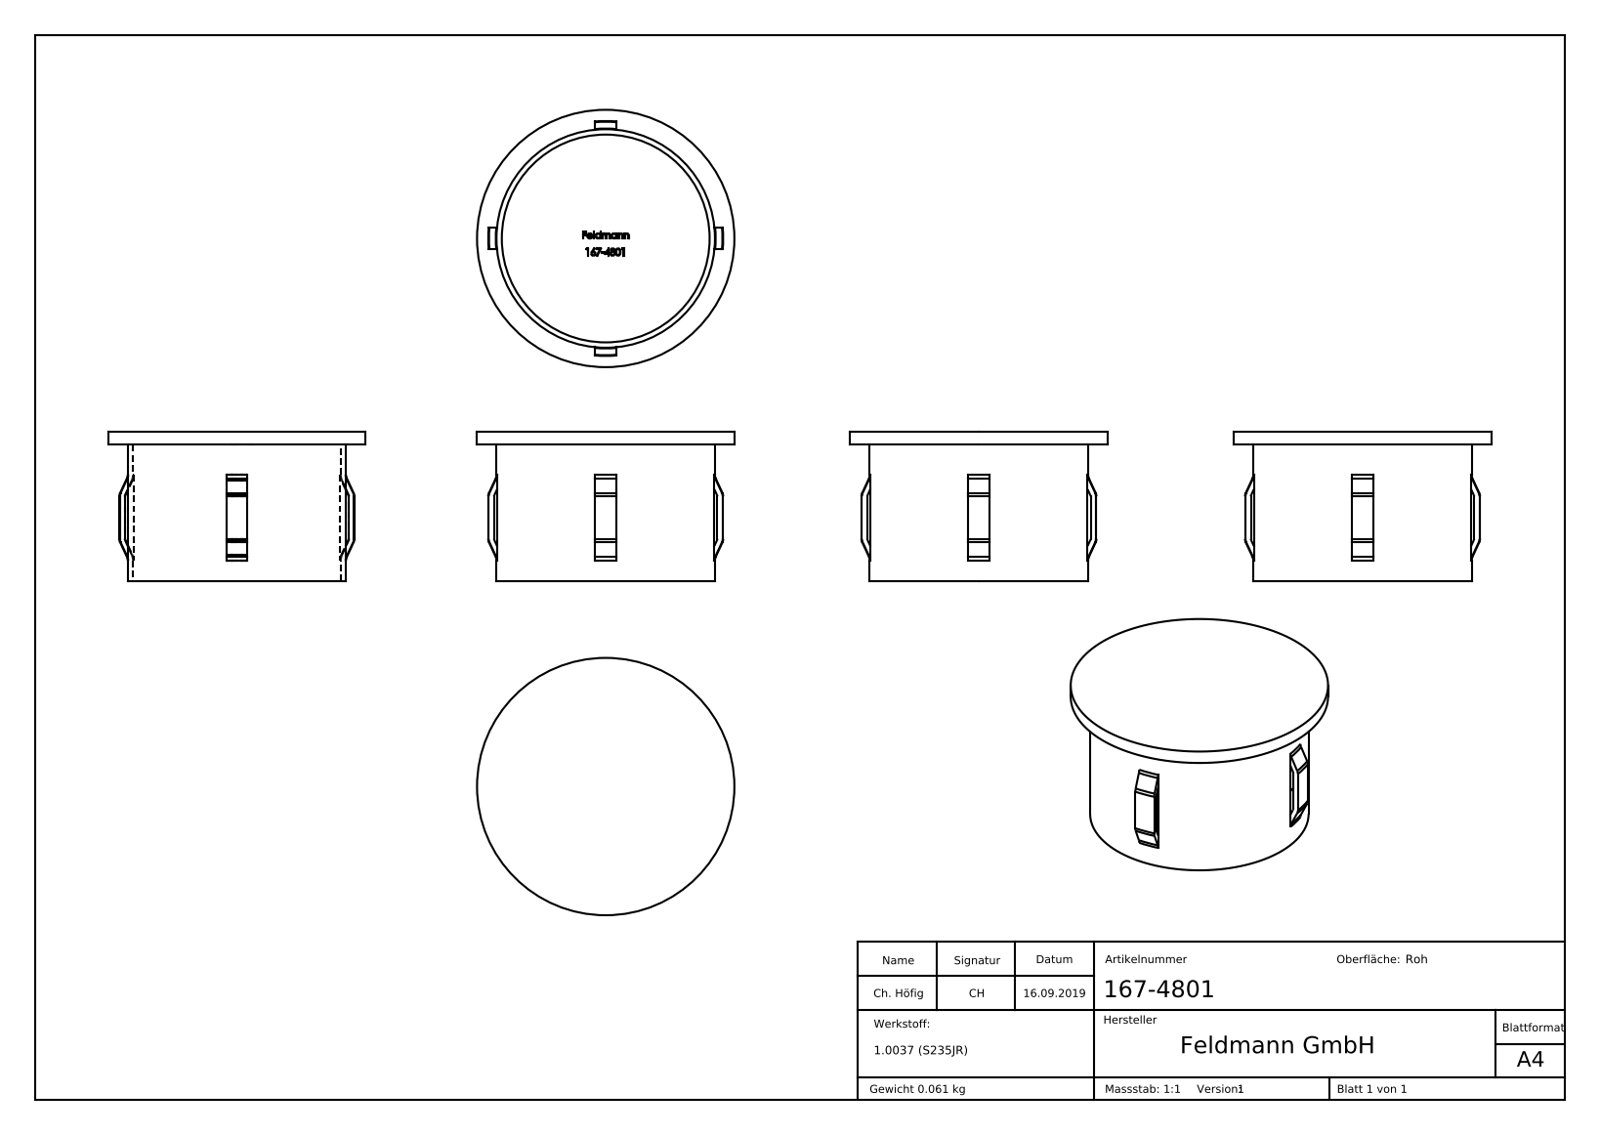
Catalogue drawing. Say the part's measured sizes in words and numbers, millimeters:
The part is named "167-4801". Its 3-D file was written by "SolidWorks 2015 (CONFIG_CONTROL_DESIGN)". It is 1 solid with 295 faces: 136 planar, 16 cylindrical and 143 other. Overall it measures 48.3 by 48.3 by 28.2 millimeters. Its volume is 7 820 cubic millimeters and its surface area 10 743 square millimeters. Round holes: 1 of diameter 39. Round bosses or shafts: 1 of diameter 48.3, 1 of diameter 41. Partial cylindrical surfaces (rounded edges, fillets, slot ends): 1 of radius 21.05, 1 of radius 22.05. The main face-to-face distances are 2.5, 25.7, 28.2, 4, 2.4, 25.8, 3.88, 2.85, 2, 1.26.
